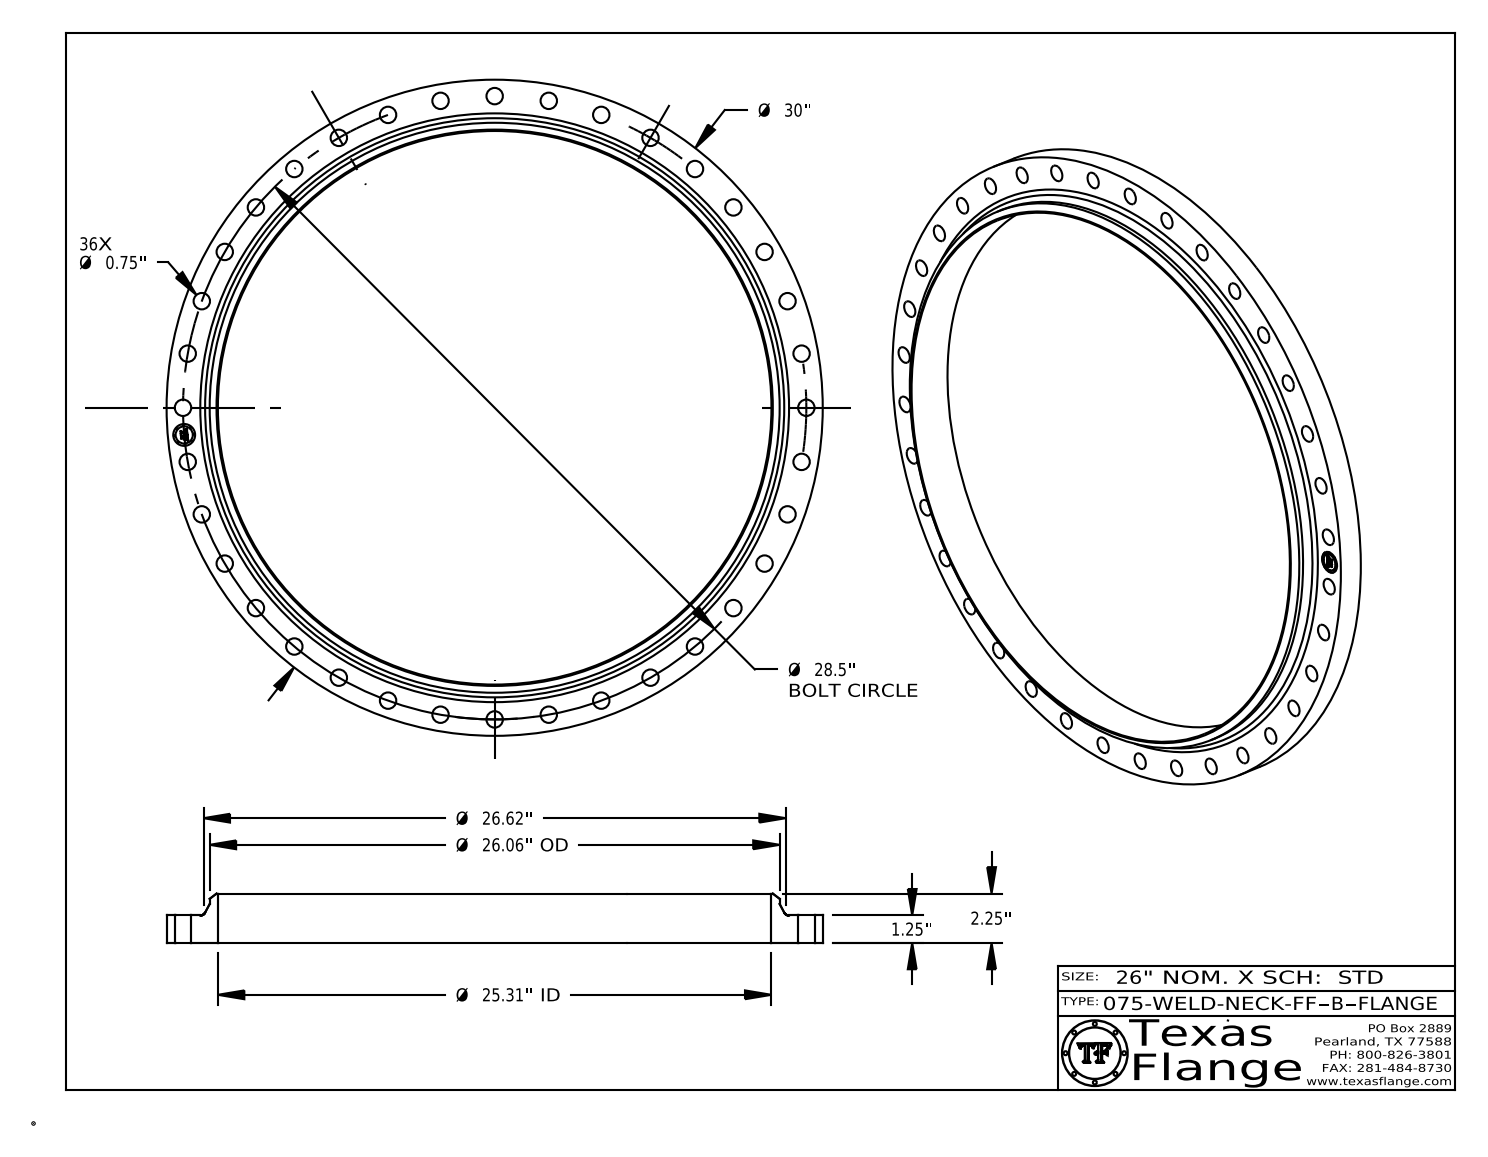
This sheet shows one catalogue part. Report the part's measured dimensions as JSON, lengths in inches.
{"part_name": "075-WELD-NECK-FF, Series B", "step_written_by": "CATIA V5 STEP AP214 (AUTOMOTIVE_DESIGN)", "units": "inches", "bodies": {"solids": 1, "faces": 472, "planar": 368, "cylindrical": 98, "other": 6}, "overall_size": [30, 30, 2.25], "volume_in3": 268.4, "surface_area_in2": 828, "round_holes": [[0.75, 36], [1, 1], [25.31, 1]], "round_bosses_or_shafts": [[0.061, 8], [30, 1], [26.06, 1], [0.788, 1]], "face_to_face_distances": [1.25, 2.25, 1, 0.015, 1.235, 1.015, 0.298, 0.292, 0.054, 0.193], "hole_center_spacings": [14.25, 21.832, 9.748, 2.484, 12.044, 25.83, 7.376, 24.682]}
